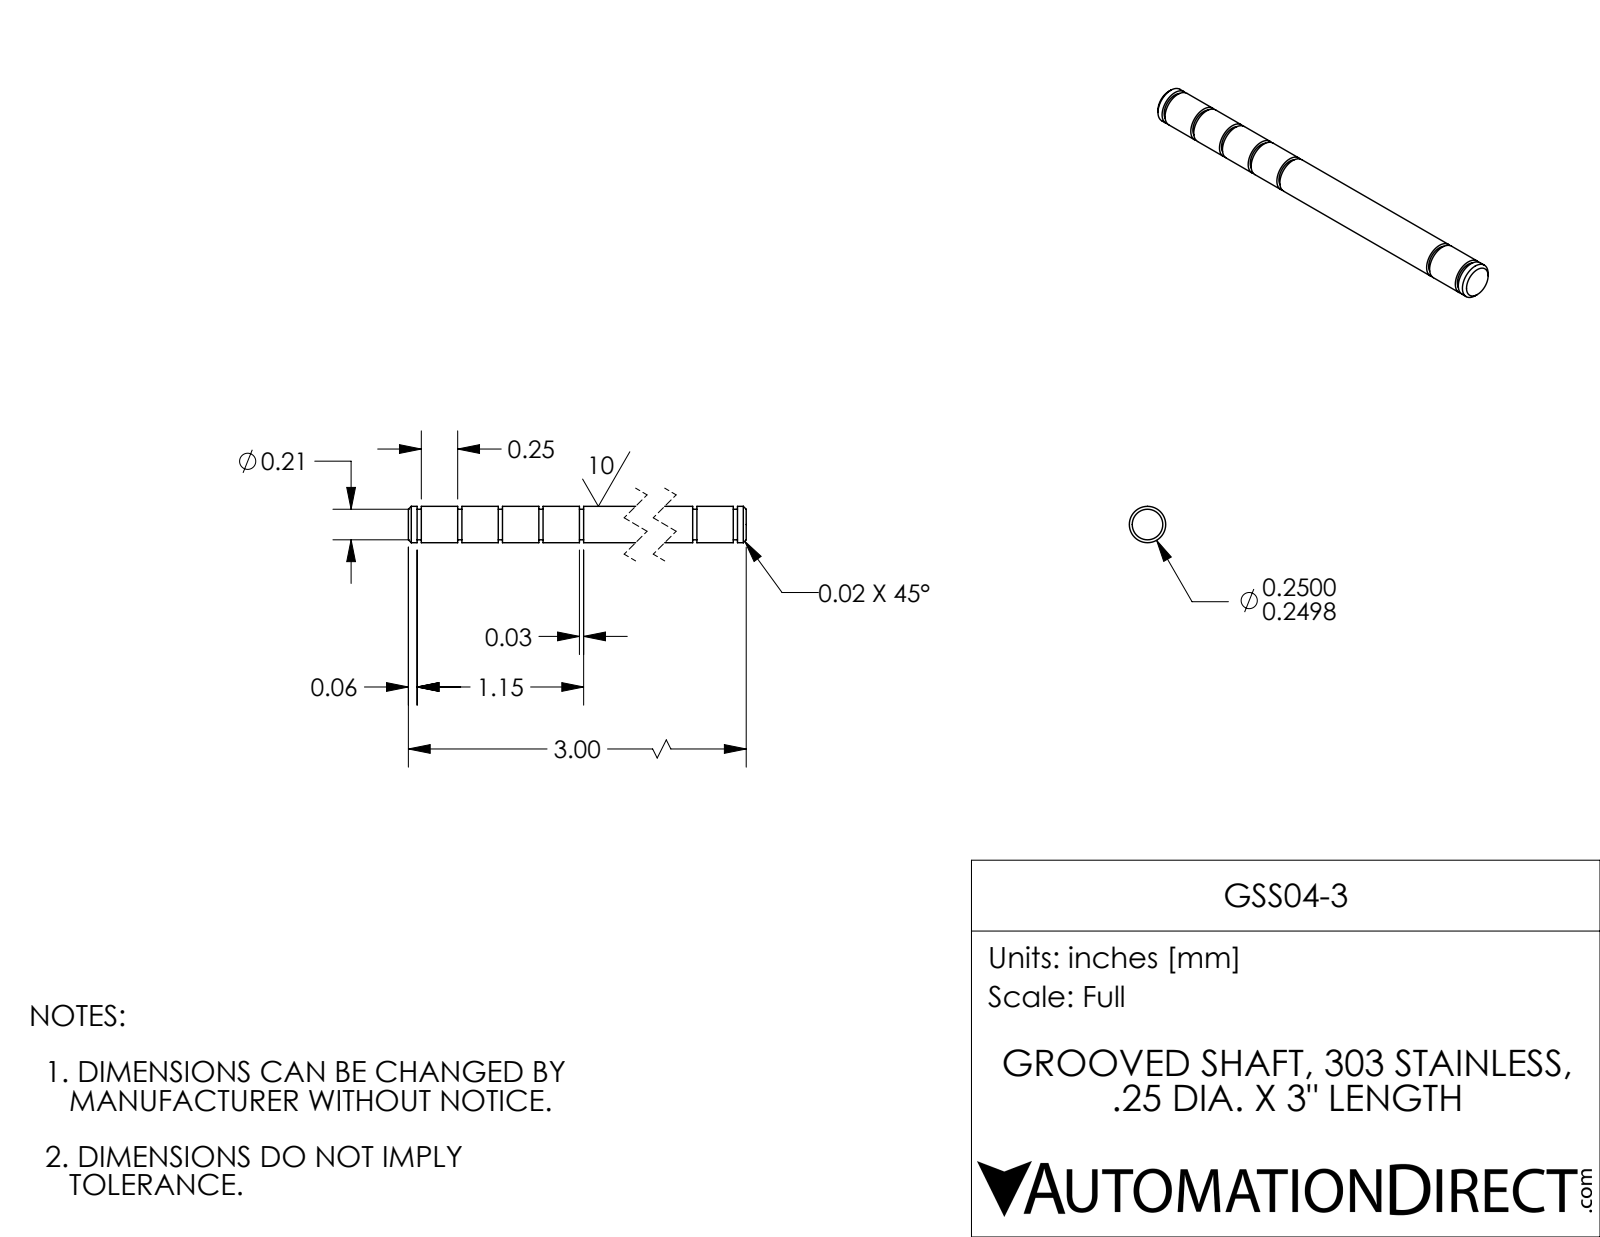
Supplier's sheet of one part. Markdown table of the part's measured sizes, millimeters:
| quantity | value |
| --- | --- |
| part name | GSS04-3 |
| STEP written by | SolidWorks 2017 (AUTOMOTIVE_DESIGN) |
| units | millimeters |
| bodies | 1 solid, 50 faces (16 planar, 30 cylindrical, 4 other) |
| overall size | 76.2 × 6.4 × 6.4 |
| volume | 2 360 mm³ |
| surface area | 1 685 mm² |
| round bosses / shafts (diameter × count) | 6.4 × 1, 5.3 × 1 |
| main face-to-face distances | 7.1, 0.7, 6.4, 21.3, 65.3, 14.2, 44.1, 58.2, 51.2, 7.8 |
